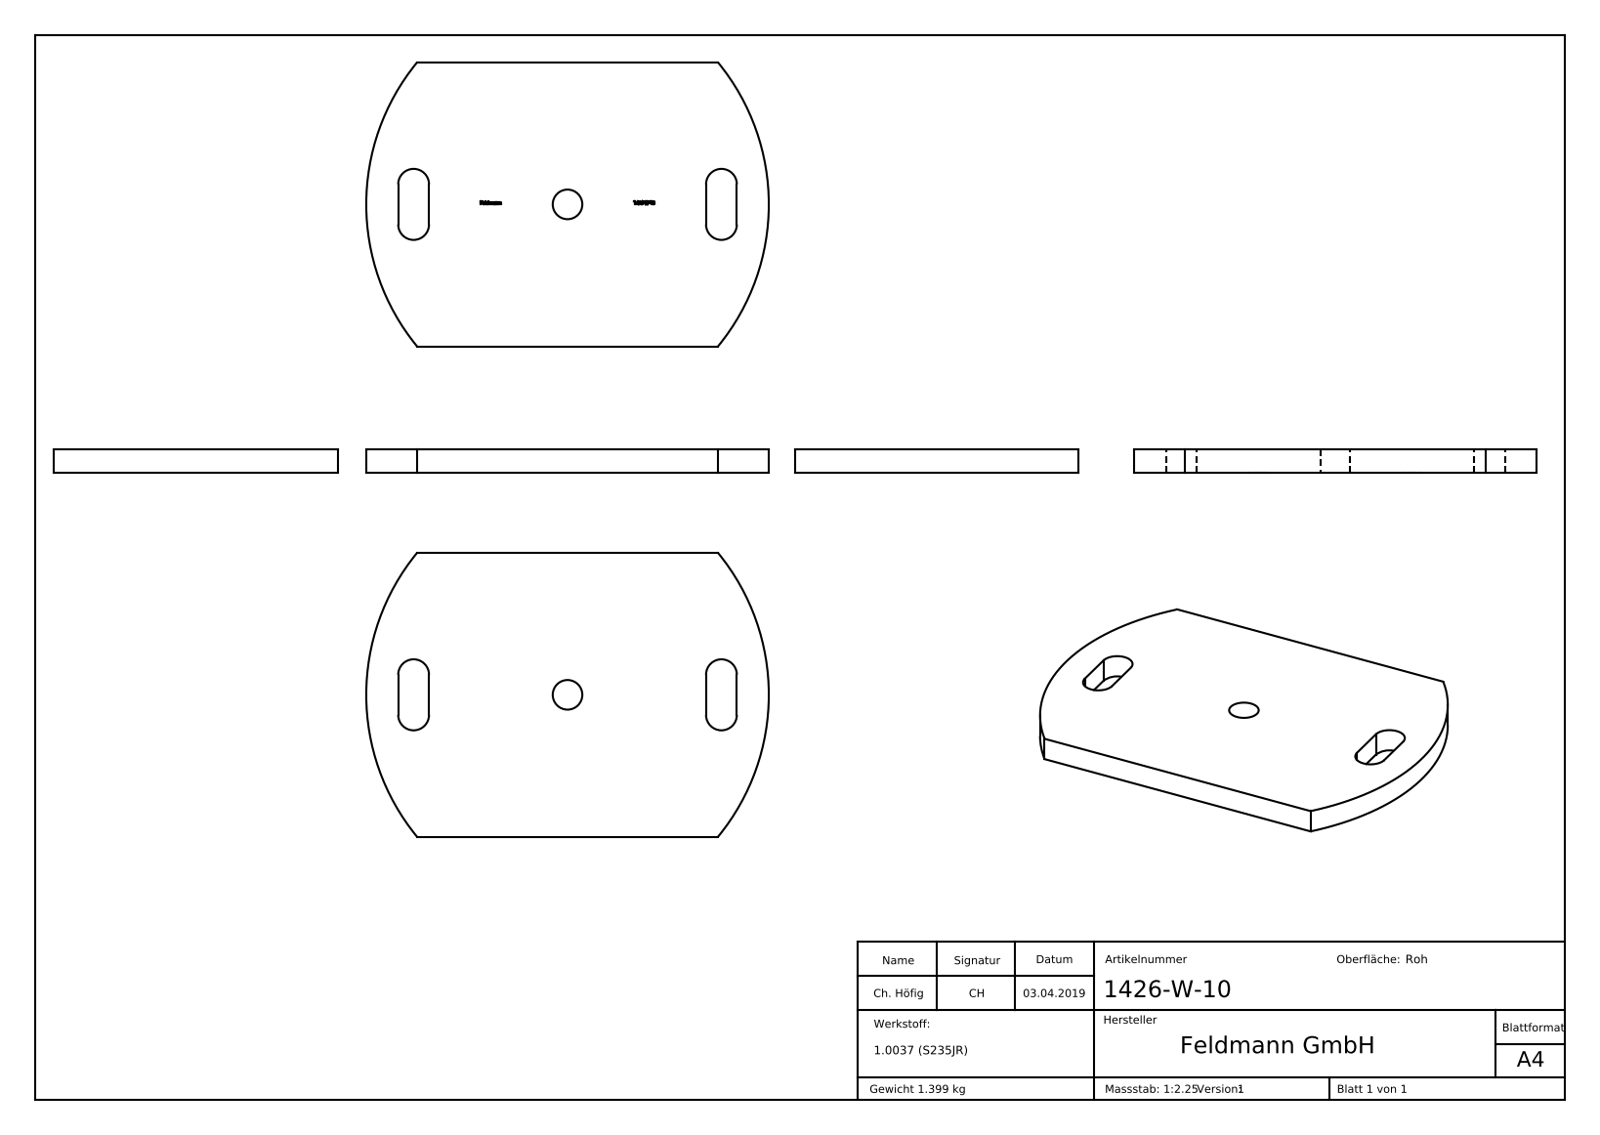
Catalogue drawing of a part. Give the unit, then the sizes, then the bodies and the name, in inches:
Units: inches
Overall size (bounding box): 6.693 × 4.724 × 0.394
Round holes (diameter × count): ⌀0.492 ×1
Partial cylindrical surfaces — rounded edges, fillets, slot ends (radius × count): R0.256 ×4, R3.719 ×2
Main face-to-face distances: 0.394, 4.724, 0.512, 5.118, 5.63, 4.606, 0.39, 2.362, 2.479, 2.754
Volume: 10.95 in³ · Surface area: 66.51 in²
Bodies: 1 solid, 222 faces (140 planar, 10 cylindrical, 72 other)
Part name (STEP PRODUCT): 1426-W-10
STEP written by: SolidWorks 2015 (CONFIG_CONTROL_DESIGN)
